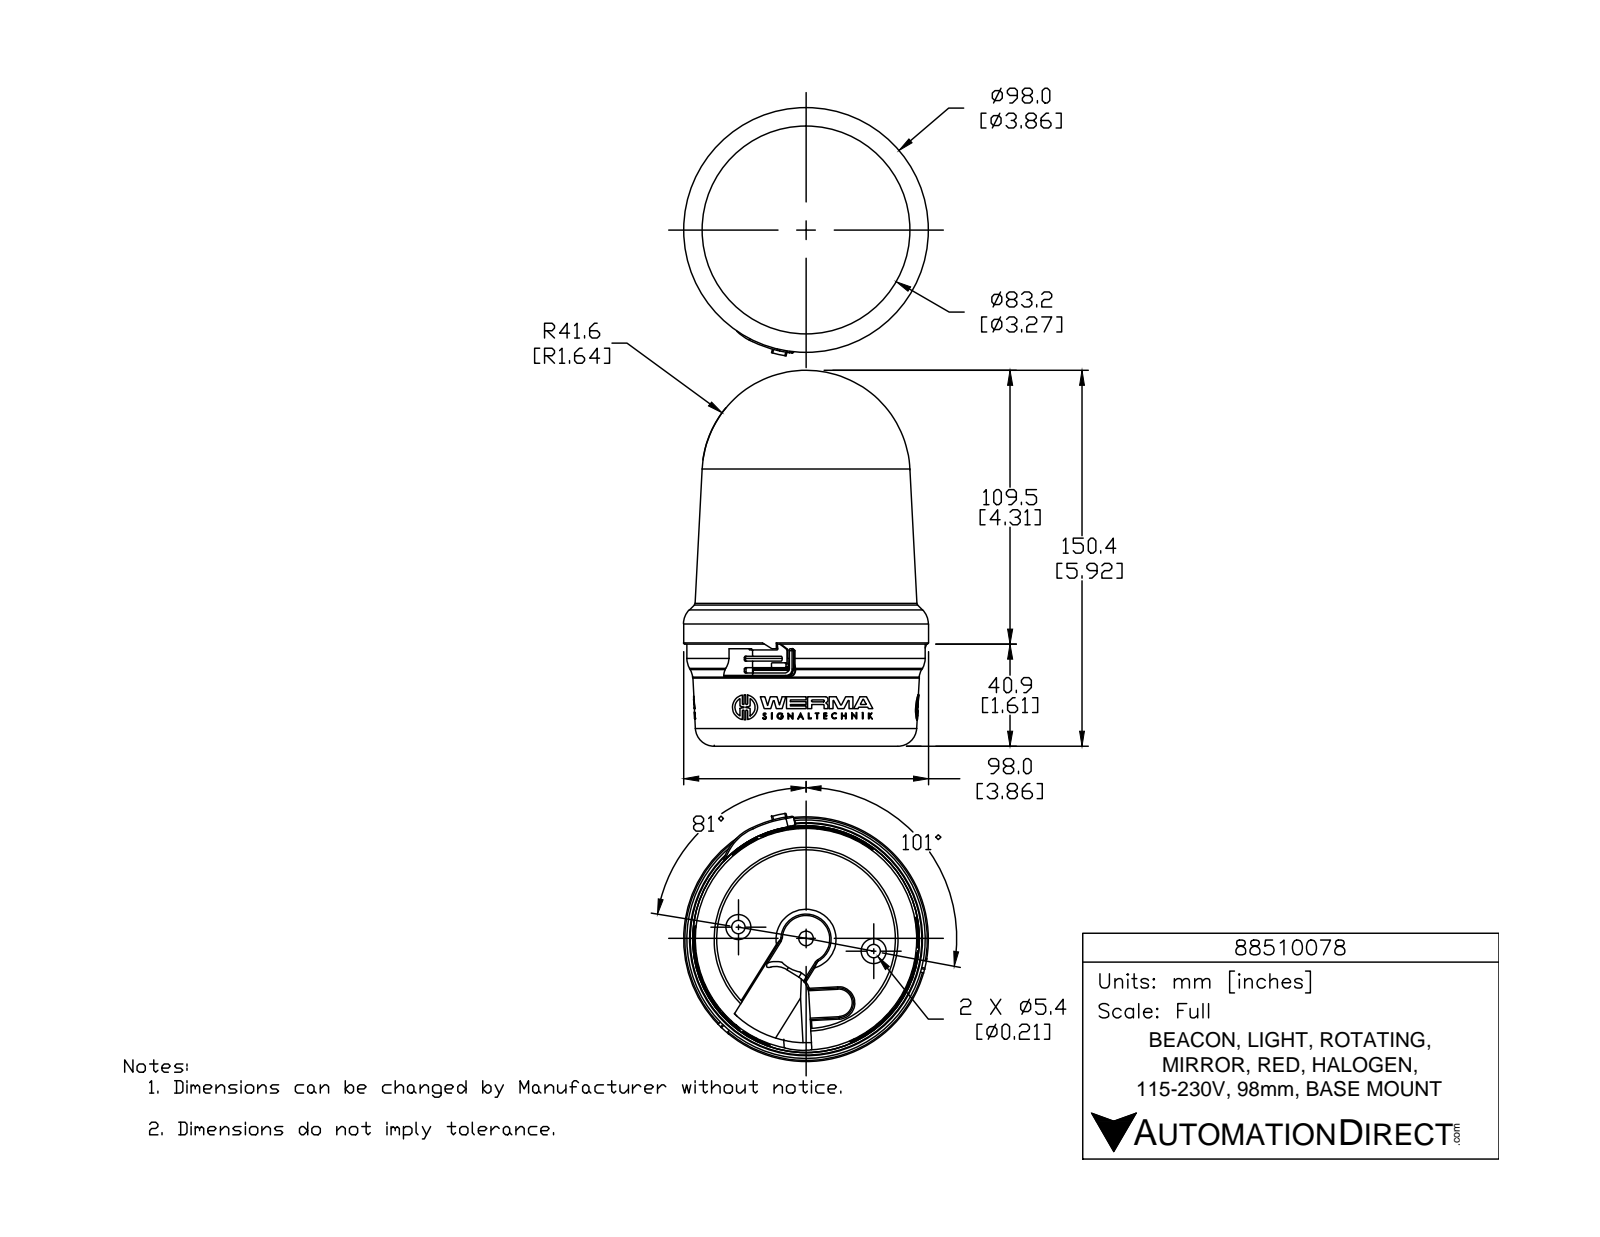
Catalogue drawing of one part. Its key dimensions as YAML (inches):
part_name: "88510078"
step_written_by: "SolidWorks 2015 (AUTOMOTIVE_DESIGN)"
units: inches
bodies: {solids: 1, faces: 969, planar: 586, cylindrical: 238, other: 145}
overall_size: [5.921, 3.912, 3.858]
volume: 49.51
surface_area: 82.1
round_holes:
  - {diameter: 0.068, count: 3}
  - {diameter: 0.213, count: 2}
  - {diameter: 0.409, count: 2}
  - {diameter: 2.815, count: 1}
round_bosses_or_shafts:
  - {diameter: 0.395, count: 3}
  - {diameter: 0.099, count: 3}
  - {diameter: 0.394, count: 2}
  - {diameter: 3.858, count: 1}
  - {diameter: 3.756, count: 1}
  - {diameter: 3.571, count: 1}
partial_cylinders:
  - {radius: 0.02, count: 21}
  - {radius: 0.006, count: 9}
  - {radius: 0.006, count: 6}
  - {radius: 0.014, count: 6}
  - {radius: 0.014, count: 6}
  - {radius: 0.014, count: 6}
  - {radius: 0.229, count: 6}
  - {radius: 0.079, count: 4}
face_to_face_distances: [0.059, 0.033, 0.27, 0.02, 0.289, 0.734, 0.768, 0.315, 1.319, 1.26]
hole_center_spacings: [1.083, 2.165]
